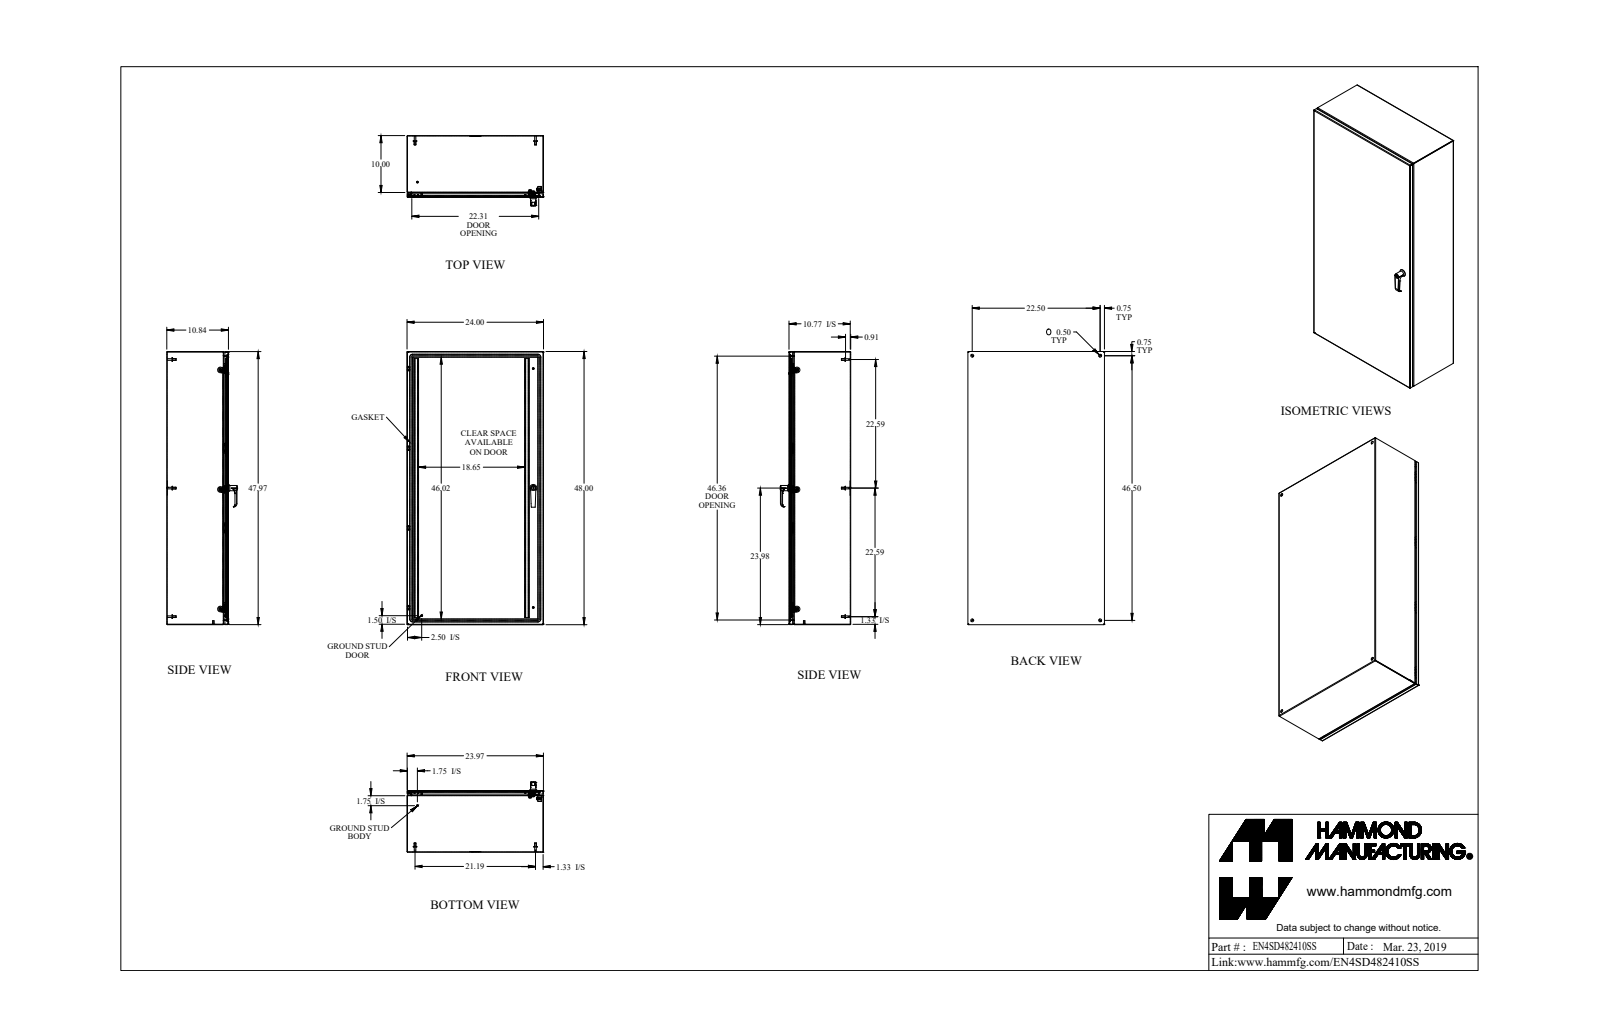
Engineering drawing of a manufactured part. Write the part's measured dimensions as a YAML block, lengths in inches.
part_name: "EN4SD482410SS"
step_written_by: "SolidWorks 2018 (AUTOMOTIVE_DESIGN)"
units: inches
bodies: {solids: 53, faces: 1469, planar: 632, cylindrical: 538, other: 299}
overall_size: [48, 24, 12.372]
volume: 319.5
surface_area: 8870
round_holes:
  - {diameter: 0.176, count: 6}
  - {diameter: 0.5, count: 4}
  - {diameter: 0.196, count: 3}
  - {diameter: 0.25, count: 3}
  - {diameter: 0.265, count: 3}
  - {diameter: 0.413, count: 3}
  - {diameter: 0.256, count: 2}
  - {diameter: 0.313, count: 2}
  - {diameter: 0.394, count: 2}
  - {diameter: 0.172, count: 1}
  - {diameter: 0.24, count: 1}
  - {diameter: 0.242, count: 1}
round_bosses_or_shafts:
  - {diameter: 0.313, count: 8}
  - {diameter: 0.25, count: 7}
  - {diameter: 0.625, count: 6}
  - {diameter: 0.375, count: 6}
  - {diameter: 0.275, count: 6}
  - {diameter: 0.156, count: 6}
  - {diameter: 1, count: 3}
  - {diameter: 0.63, count: 2}
partial_cylinders:
  - {radius: 0.036, count: 20}
  - {radius: 0.108, count: 20}
  - {radius: 0.03, count: 15}
  - {radius: 0.01, count: 12}
  - {radius: 0.048, count: 12}
  - {radius: 0.006, count: 8}
  - {radius: 0.04, count: 8}
  - {radius: 0.062, count: 8}
face_to_face_distances: [0.072, 10.77, 10.698, 10.842, 23.928, 23.856, 24, 0.072, 47.928, 47.928]
hole_center_spacings: [21, 21.558, 22.5, 42, 46.5, 51.657, 0.772, 0.782]
